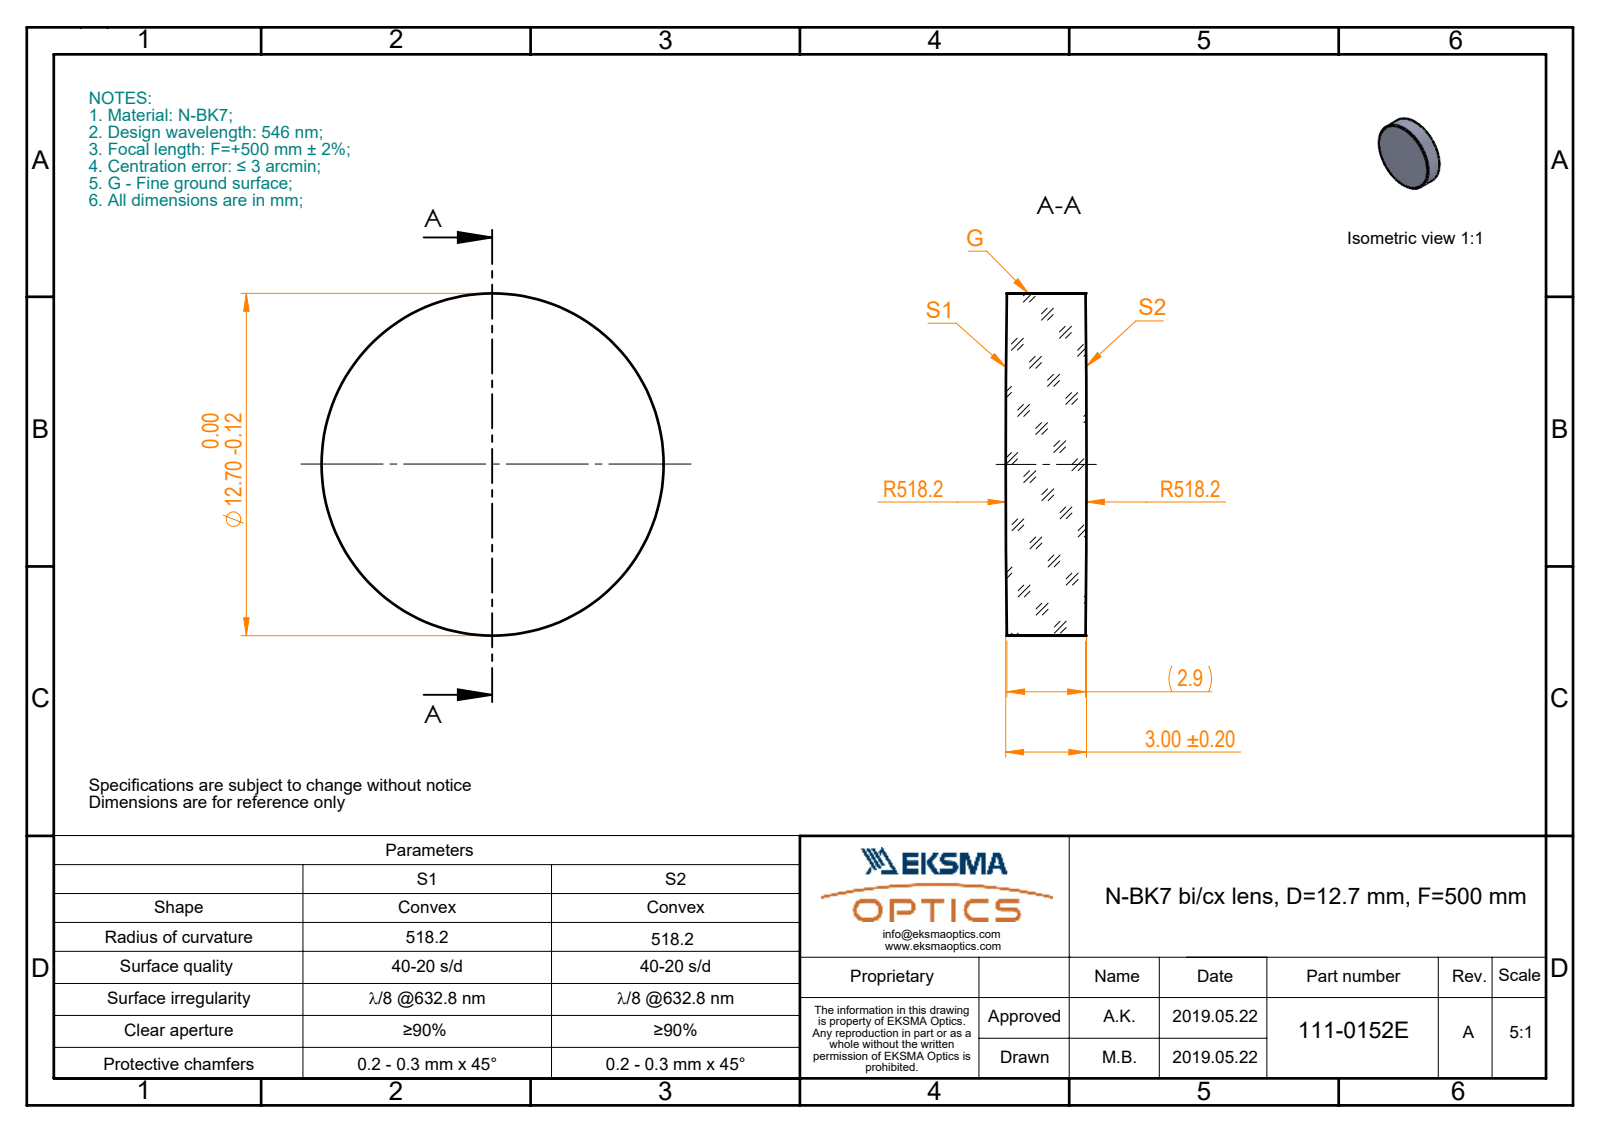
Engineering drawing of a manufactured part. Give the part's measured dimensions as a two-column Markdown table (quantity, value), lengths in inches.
| quantity | value |
| --- | --- |
| part name | 111-0152E BK7 bi-cx 12.7 F500 |
| STEP written by | SolidWorks 2017 (CONFIG_CONTROL_DESIGN) |
| units | inches |
| bodies | 1 solid, 6 faces (0 planar, 2 cylindrical, 4 other) |
| overall size | 0.5 × 0.5 × 0.118 |
| volume | 0.023 in³ |
| surface area | 0.574 in² |
| round bosses / shafts (diameter × count) | 0.5 × 1 |
